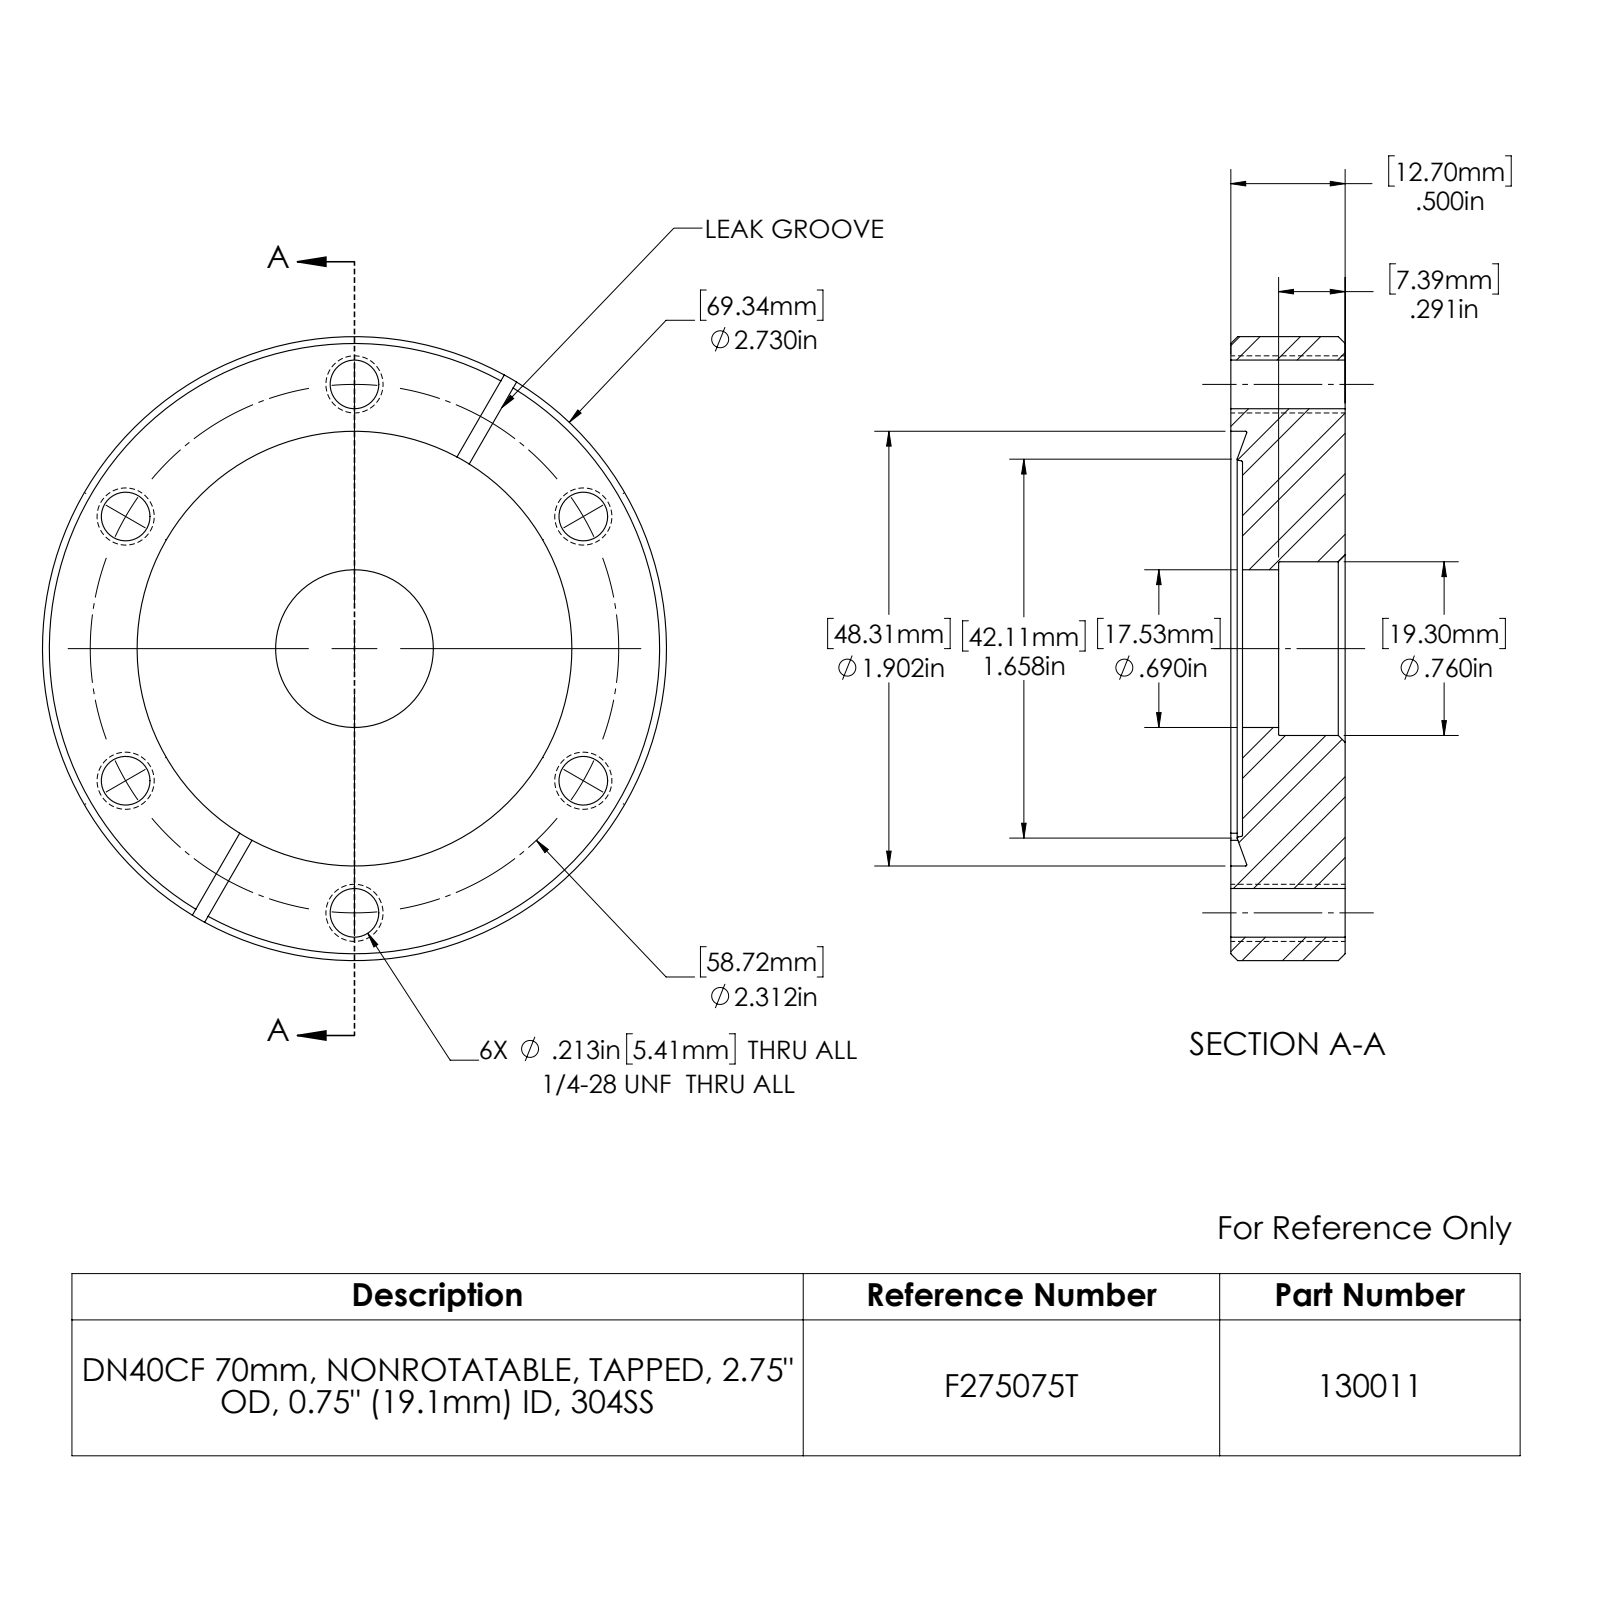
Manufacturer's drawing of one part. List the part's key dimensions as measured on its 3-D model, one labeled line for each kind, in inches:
Part name (STEP PRODUCT): 130011_D
STEP written by: SolidWorks 2022 (CONFIG_CONTROL_DESIGN)
Units: inches
Bodies: 1 solid, 50 faces (11 planar, 20 cylindrical, 19 other)
Overall size (bounding box): 2.73 × 2.73 × 0.5
Volume: 2.474 in³ · Surface area: 18.12 in²
Round holes (diameter × count): ⌀0.213 ×6, ⌀0.69 ×1, ⌀0.76 ×1, ⌀1.902 ×1
Round bosses / shafts (diameter × count): ⌀2.73 ×1
Main face-to-face distances: 0.5, 0.051, 0.449, 0.209, 0.158, 0.291, 0.052, 0.157, 0.448, 0.062
Hole centre spacings: 1.156, 2.002, 2.002, 2.312, 2.312
